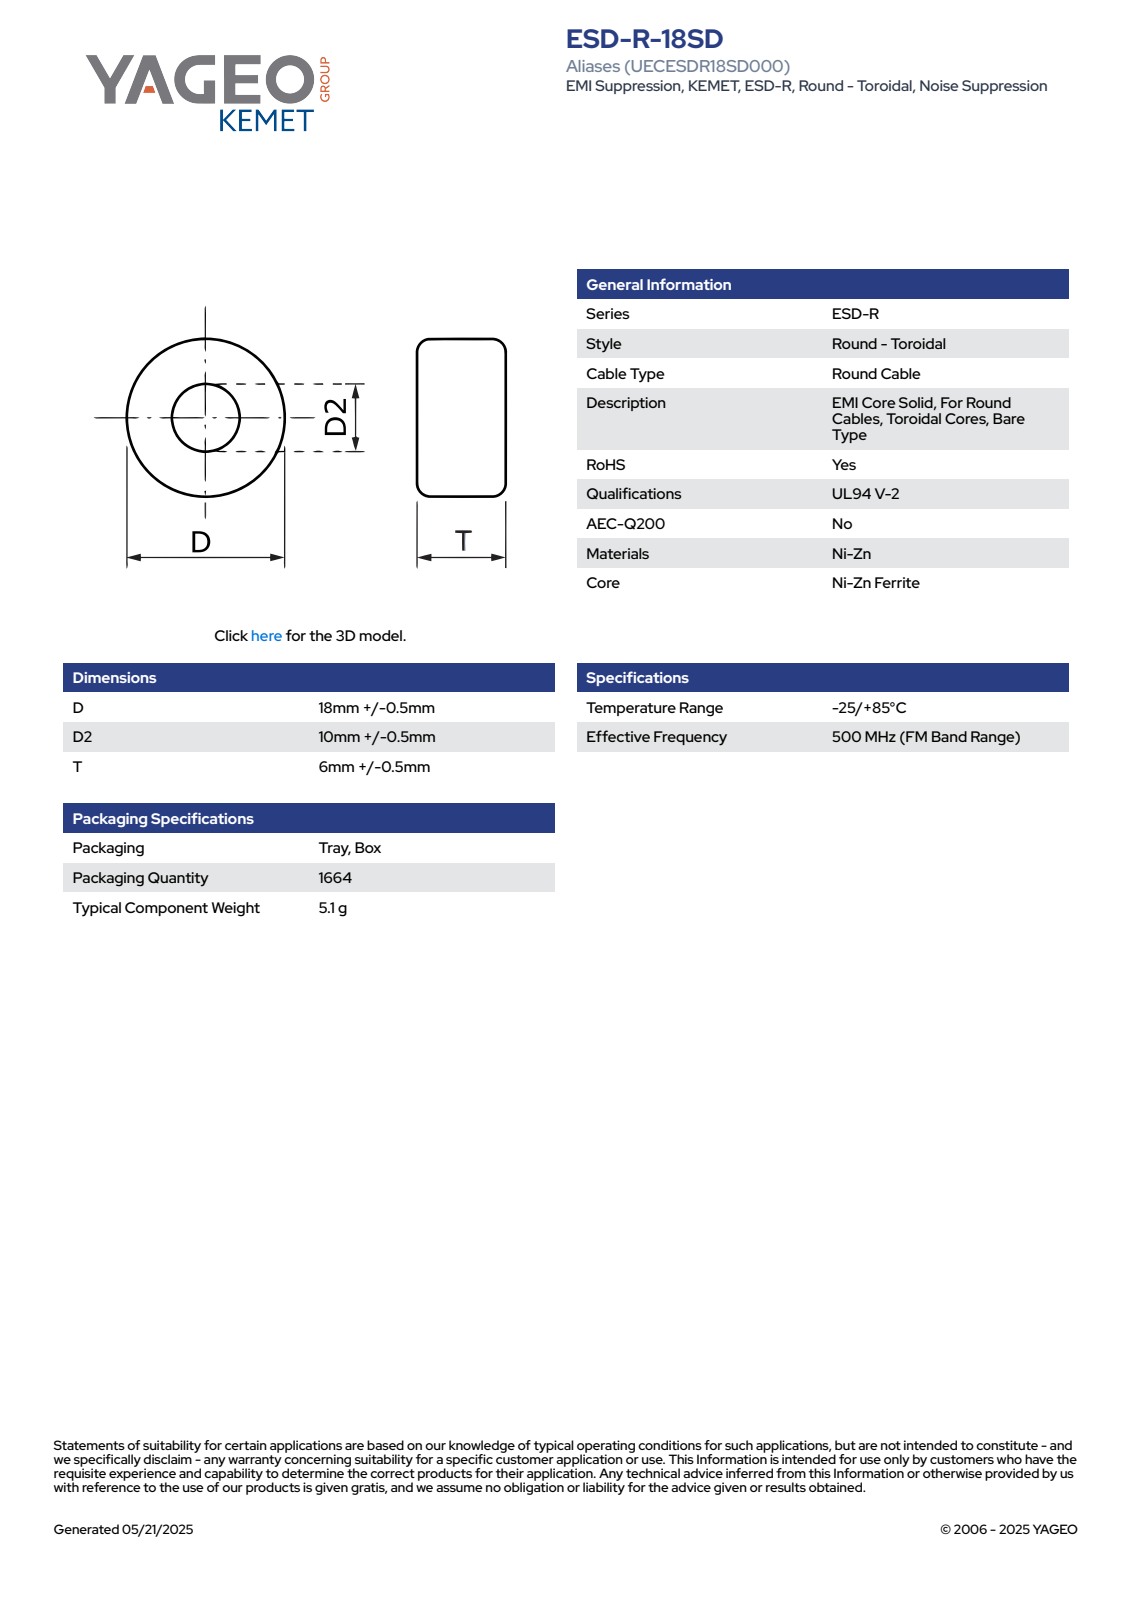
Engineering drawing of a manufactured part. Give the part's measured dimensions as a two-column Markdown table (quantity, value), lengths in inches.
| quantity | value |
| --- | --- |
| part name | EC_KBC_D18.5D210T6.5 |
| STEP written by | SolidWorks 2021 (AUTOMOTIVE_DESIGN) |
| units | inches |
| bodies | 1 solid, 66 faces (24 planar, 7 cylindrical, 35 other) |
| overall size | 0.729 × 0.728 × 0.256 |
| volume | 0.075 in³ |
| surface area | 1.45 in² |
| round holes (diameter × count) | 0.394 × 1 |
| round bosses / shafts (diameter × count) | 0.728 × 1 |
| partial cylindrical surfaces (radius × count) | 0.365 × 1 |
| main face-to-face distances | 0.256, 0.094, 0.161, 0.067, 0.013, 0.107, 0.149, 0.054, 0.042, 0.136 |
